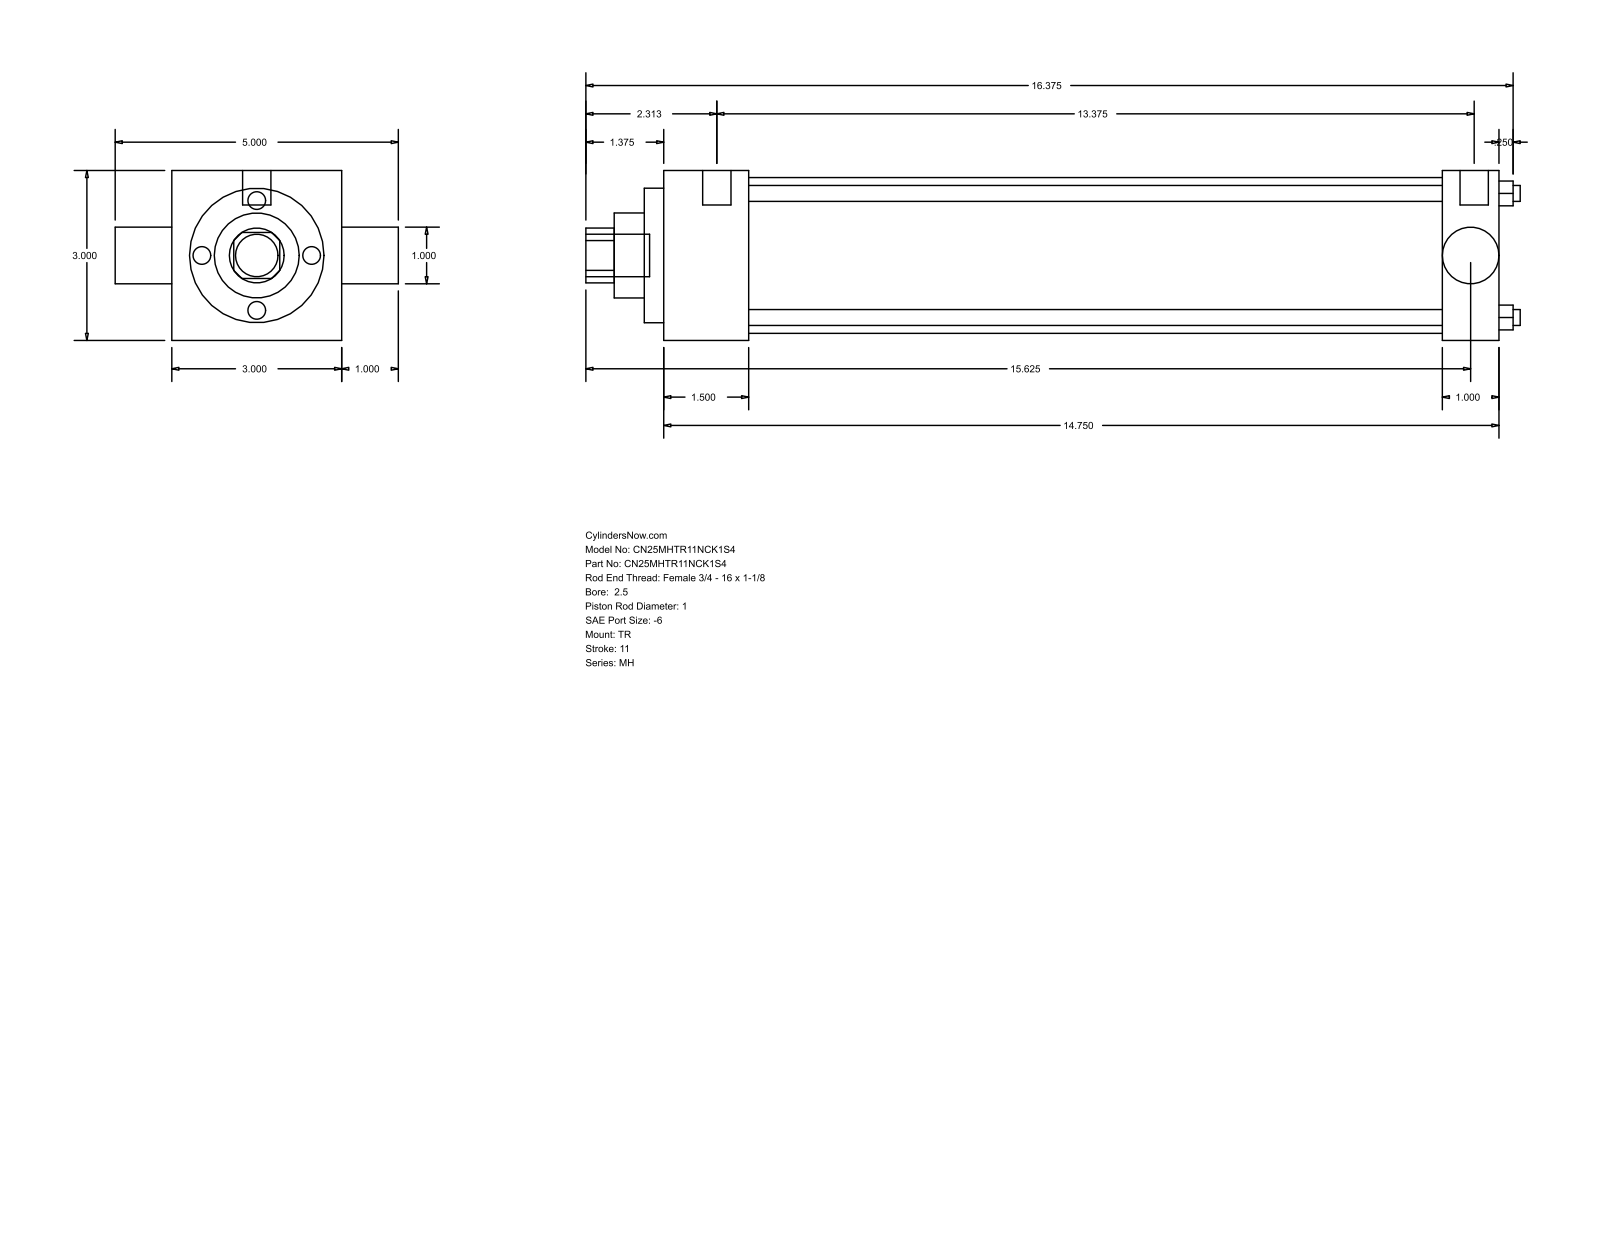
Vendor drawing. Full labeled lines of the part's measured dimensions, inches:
Part name (STEP PRODUCT): MH_TR__0250_1
STEP written by: GSSL Pune (CONFIG_CONTROL_DESIGN)
Units: inches
Bodies: 0 solids, 86 faces (61 planar, 25 cylindrical, 0 other)
Overall size (bounding box): 16.5 × 5 × 3
Round holes (diameter × count): ⌀0.281 ×4, ⌀0.998 ×1, ⌀1 ×1, ⌀1.5 ×1, ⌀2.375 ×1, ⌀2.75 ×1
Round bosses / shafts (diameter × count): ⌀0.219 ×3, ⌀0.5 ×2, ⌀0.75 ×1
Partial cylindrical surfaces — rounded edges, fillets, slot ends (radius × count): R0.484 ×1
Main face-to-face distances: 3, 14.75, 1, 1.5, 13.25, 13.75, 12.25, 0.344, 1.844, 14.094
Hole centre spacings: 1.548, 2.19, 3.097
